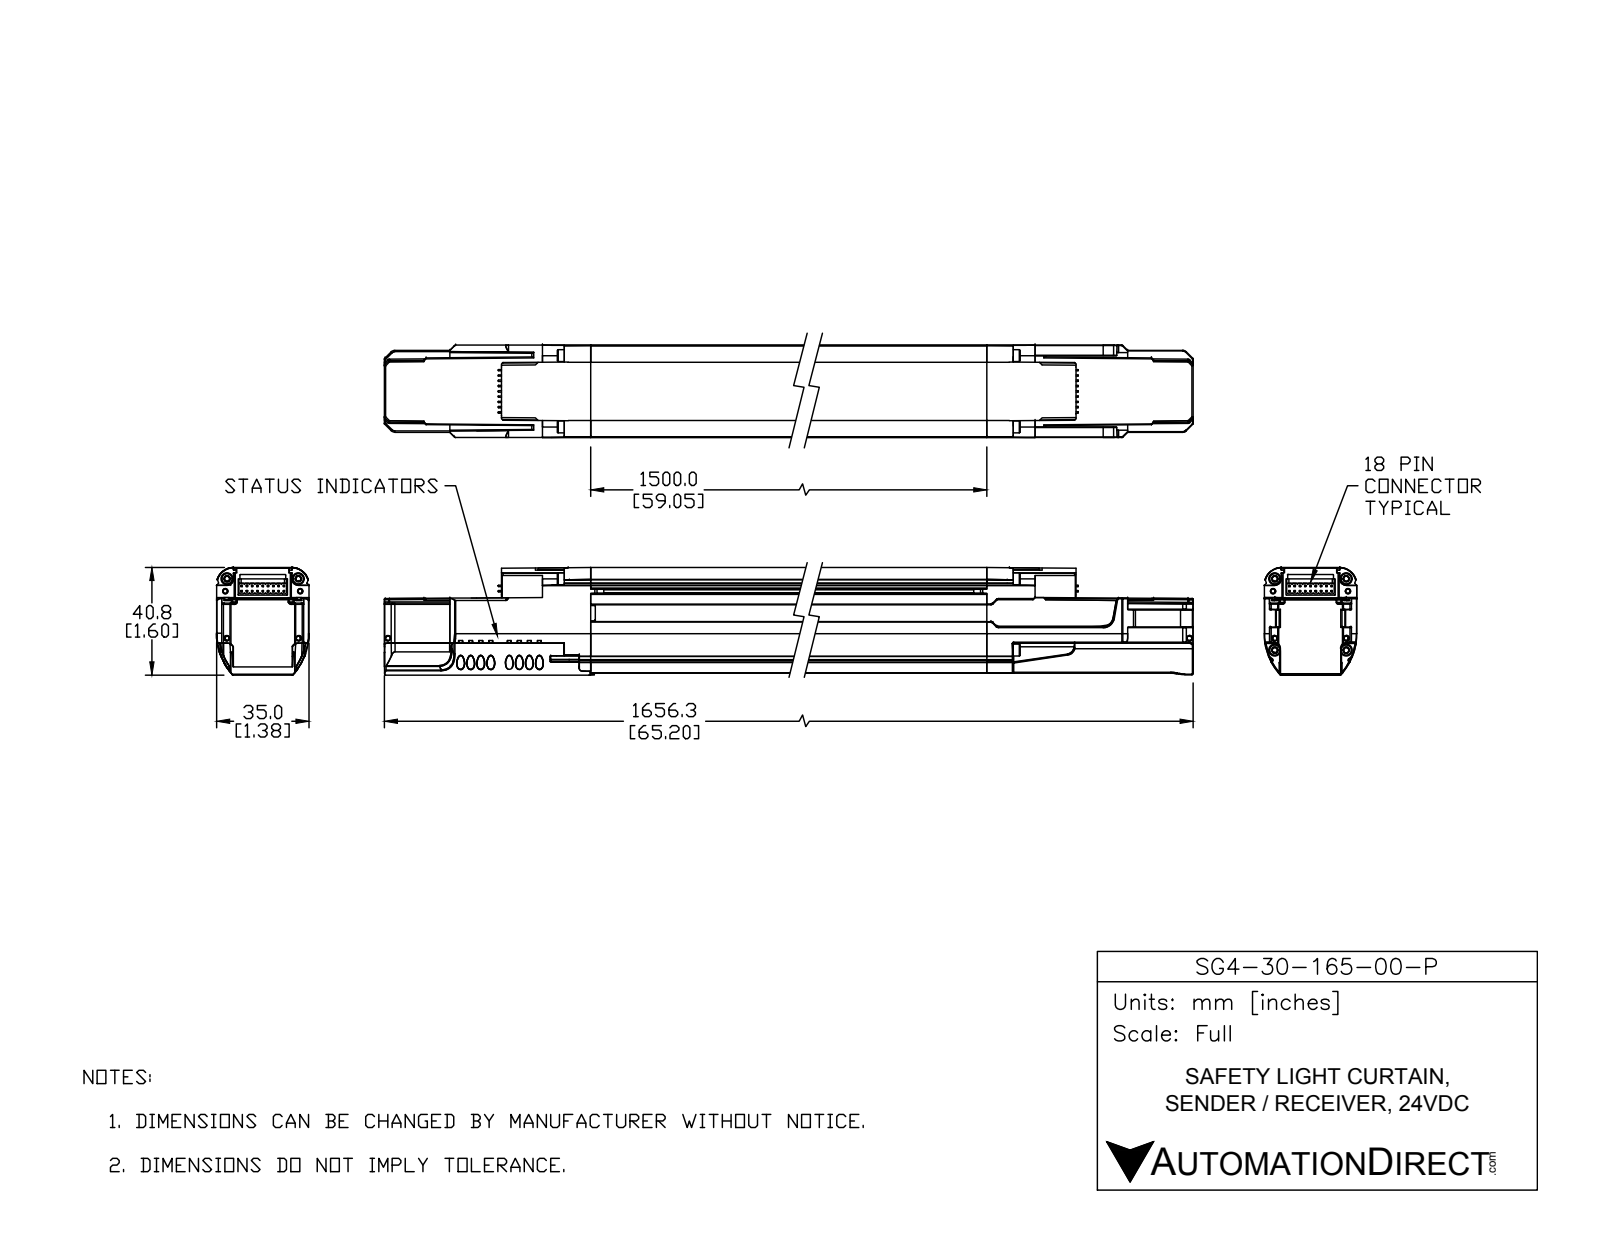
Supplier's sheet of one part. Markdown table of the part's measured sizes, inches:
| quantity | value |
| --- | --- |
| part name | SG4-30-165-OO-P |
| STEP written by | SolidWorks 2017 (AUTOMOTIVE_DESIGN) |
| units | inches |
| bodies | 16 solids, 534 faces (362 planar, 110 cylindrical, 62 other) |
| overall size | 65.203 × 2.58 × 2.023 |
| volume | 124.8 in³ |
| surface area | 684.5 in² |
| round holes (diameter × count) | 0.07 × 6, 0.1 × 4, 0.165 × 4, 0.209 × 4, 0.26 × 4, 0.065 × 1, 0.065 × 1 |
| round bosses / shafts (diameter × count) | 0.394 × 4, 0.197 × 4 |
| partial cylindrical surfaces (radius × count) | 0.106 × 16, 0.118 × 8, 0.1 × 4, 0.11 × 4, 0.08 × 2, 0.12 × 2, 0.123 × 2, 0.125 × 2 |
| main face-to-face distances | 0.06, 0.084, 0.024, 1.49, 1.466, 1.55, 1.057, 0.335, 0.481, 0.985 |
| hole center spacings | 0.569, 57.473, 0.02, 0.204, 0.207, 0.207, 0.227, 0.71 |
